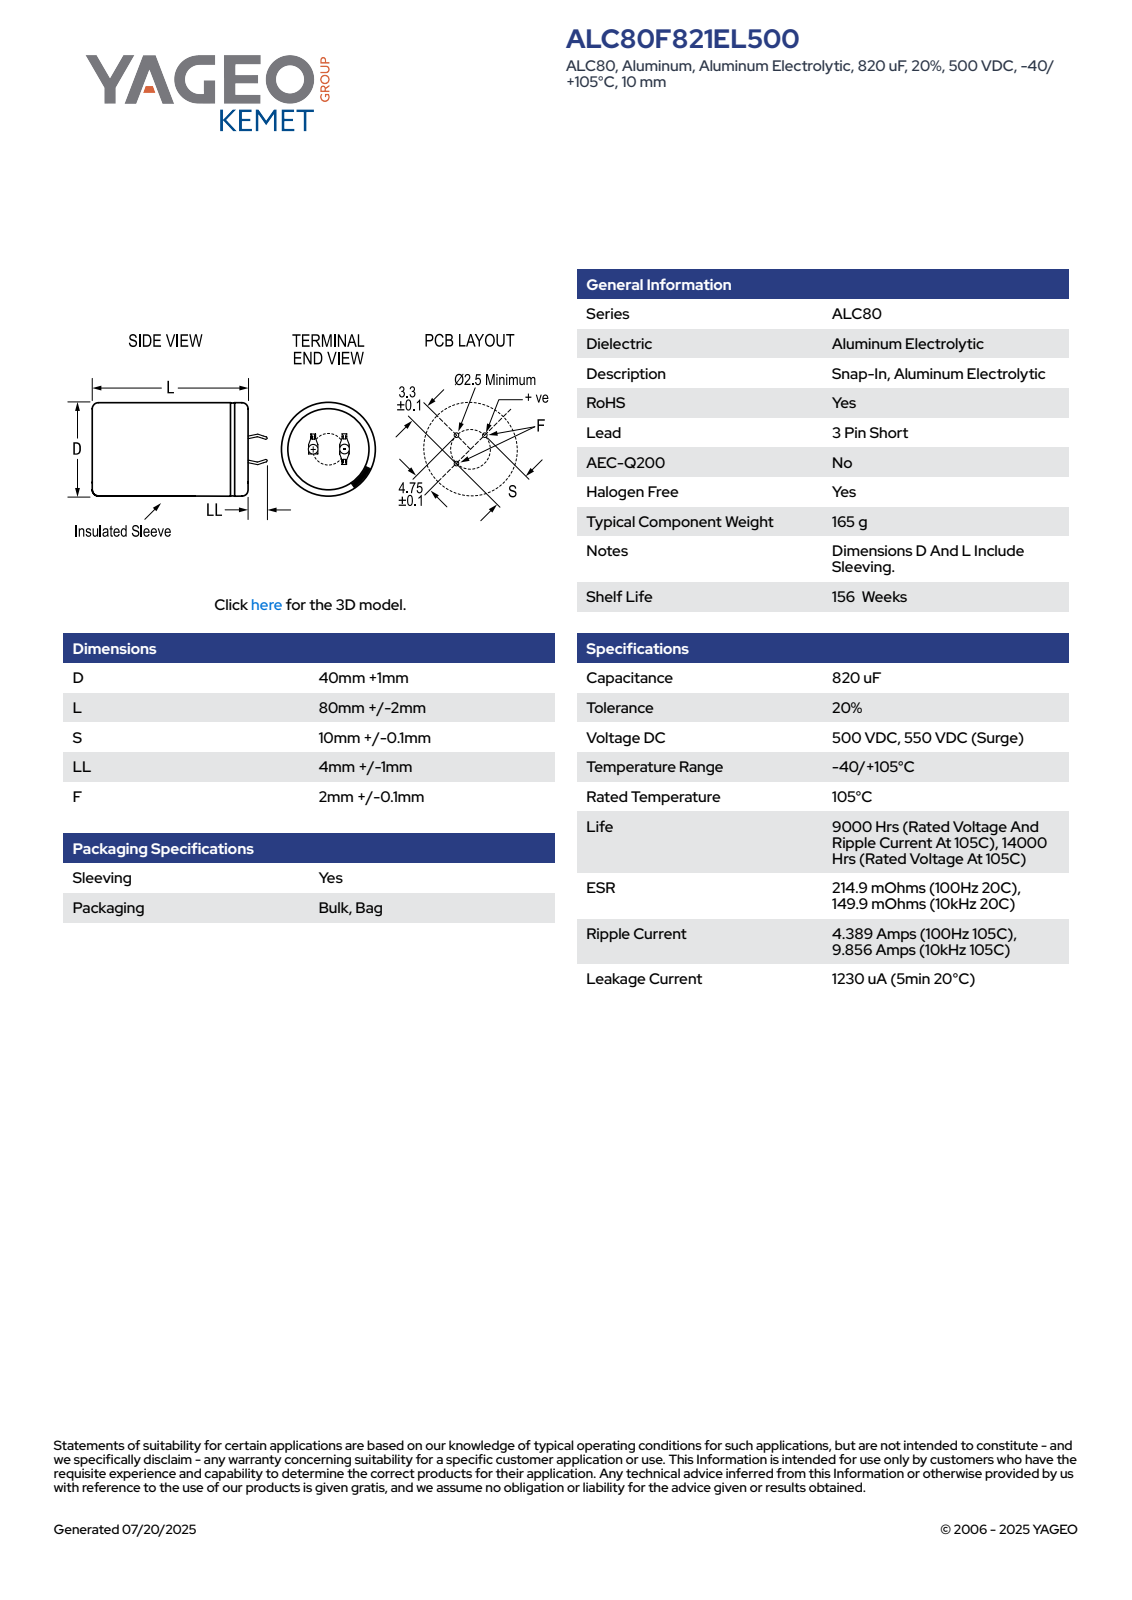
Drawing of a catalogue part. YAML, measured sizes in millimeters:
part_name: "CARS_K3P_40X80_D41L82S10LL5F2.1"
step_written_by: "SolidWorks 2014 (AUTOMOTIVE_DESIGN)"
units: millimeters
bodies: {solids: 1, faces: 115, planar: 61, cylindrical: 15, other: 39}
overall_size: [86.99, 41, 41]
volume: 107476
surface_area: 13185
round_holes:
  - {diameter: 36.28, count: 1}
round_bosses_or_shafts:
  - {diameter: 41, count: 1}
partial_cylinders:
  - {radius: 20.49, count: 1}
face_to_face_distances: [81.99, 82.49, 0.5, 0.6, 8.22, 0.59, 0.75, 1.35, 6.5, 7.47]
